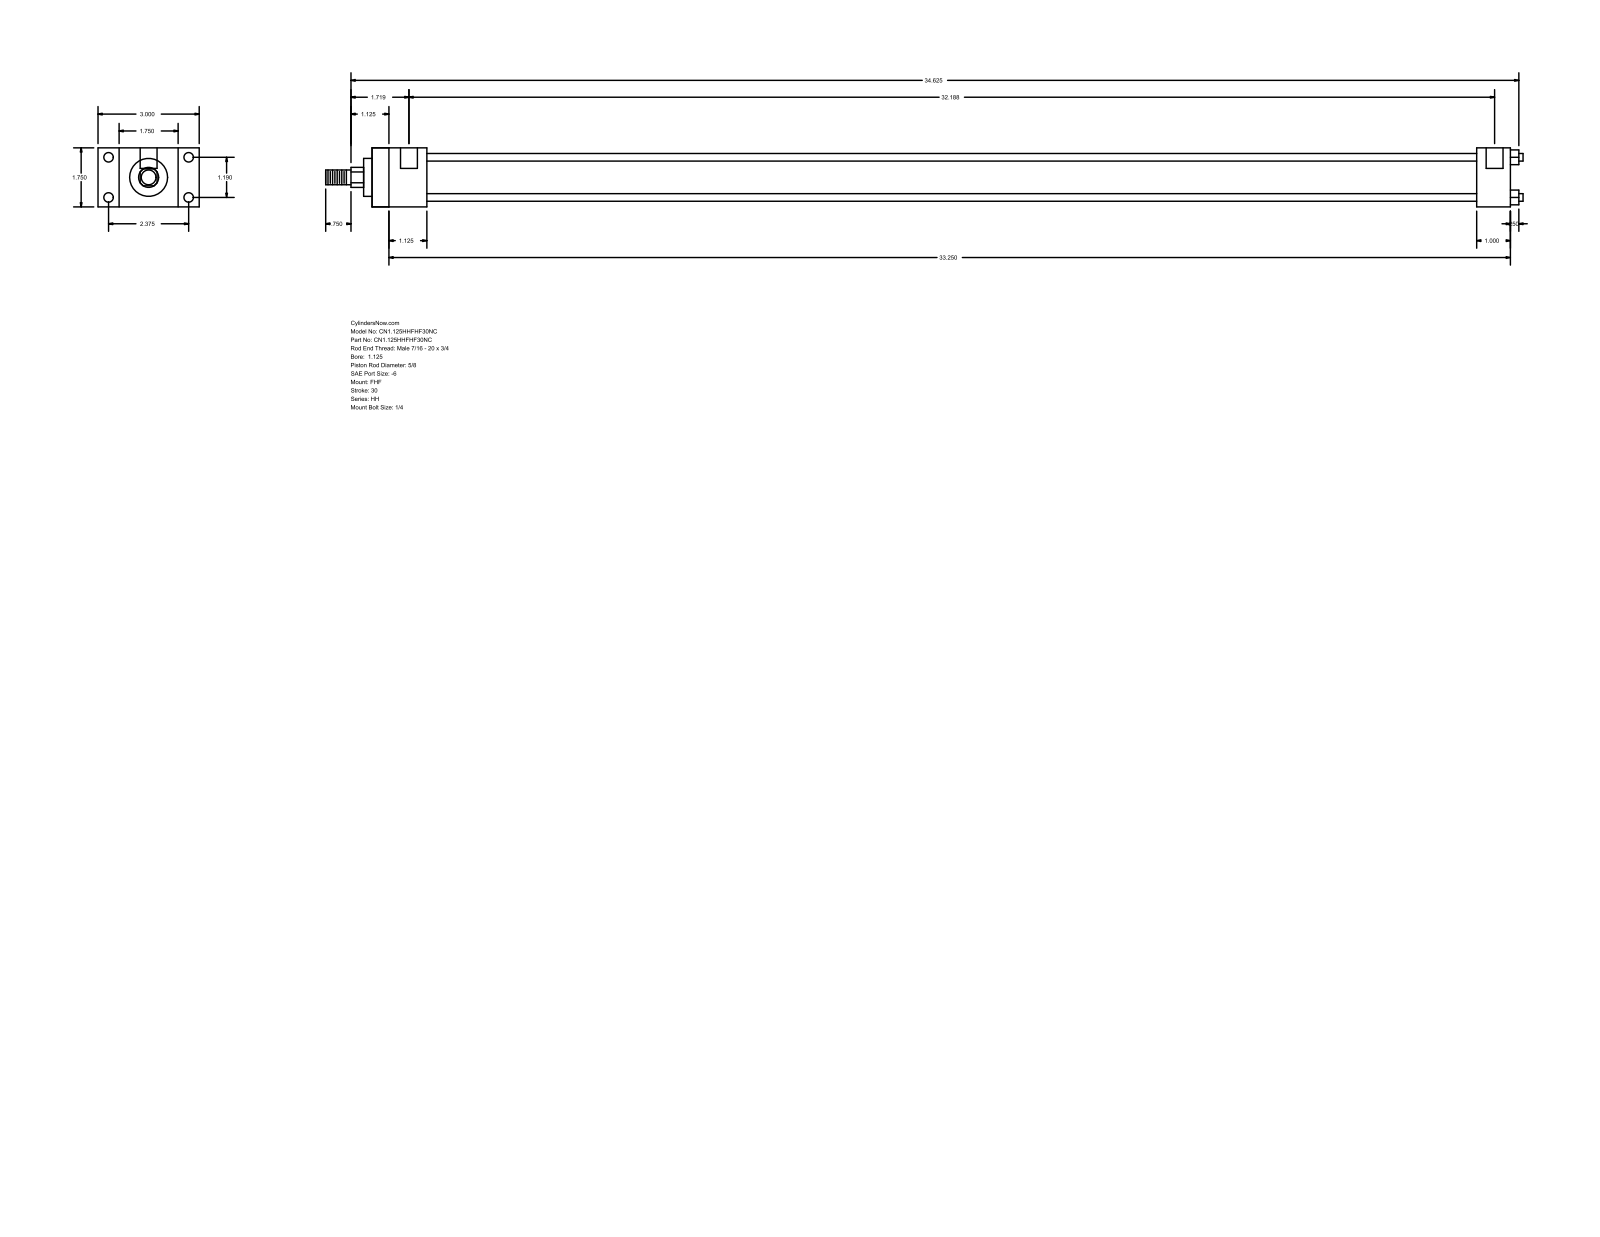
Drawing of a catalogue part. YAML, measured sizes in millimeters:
part_name: "HH_FHF__0112_0.625"
step_written_by: "GSSL Pune (CONFIG_CONTROL_DESIGN)"
units: millimeters
bodies: {solids: 0, faces: 88, planar: 60, cylindrical: 28, other: 0}
overall_size: [901.7, 76.2, 44.45]
round_holes:
  - {diameter: 5.56, count: 4}
  - {diameter: 7.14, count: 4}
  - {diameter: 12.7, count: 2}
round_bosses_or_shafts:
  - {diameter: 5.71, count: 4}
  - {diameter: 34.92, count: 1}
  - {diameter: 28.57, count: 1}
  - {diameter: 15.88, count: 1}
  - {diameter: 11.11, count: 1}
partial_cylinders:
  - {radius: 7.54, count: 1}
face_to_face_distances: [44.46, 15.87, 60.33, 41.27, 76.2, 857.24, 815.97, 831.85, 790.58, 25.39]
hole_center_spacings: [30.22, 60.32, 67.47, 814.39, 3.17, 817.56]
